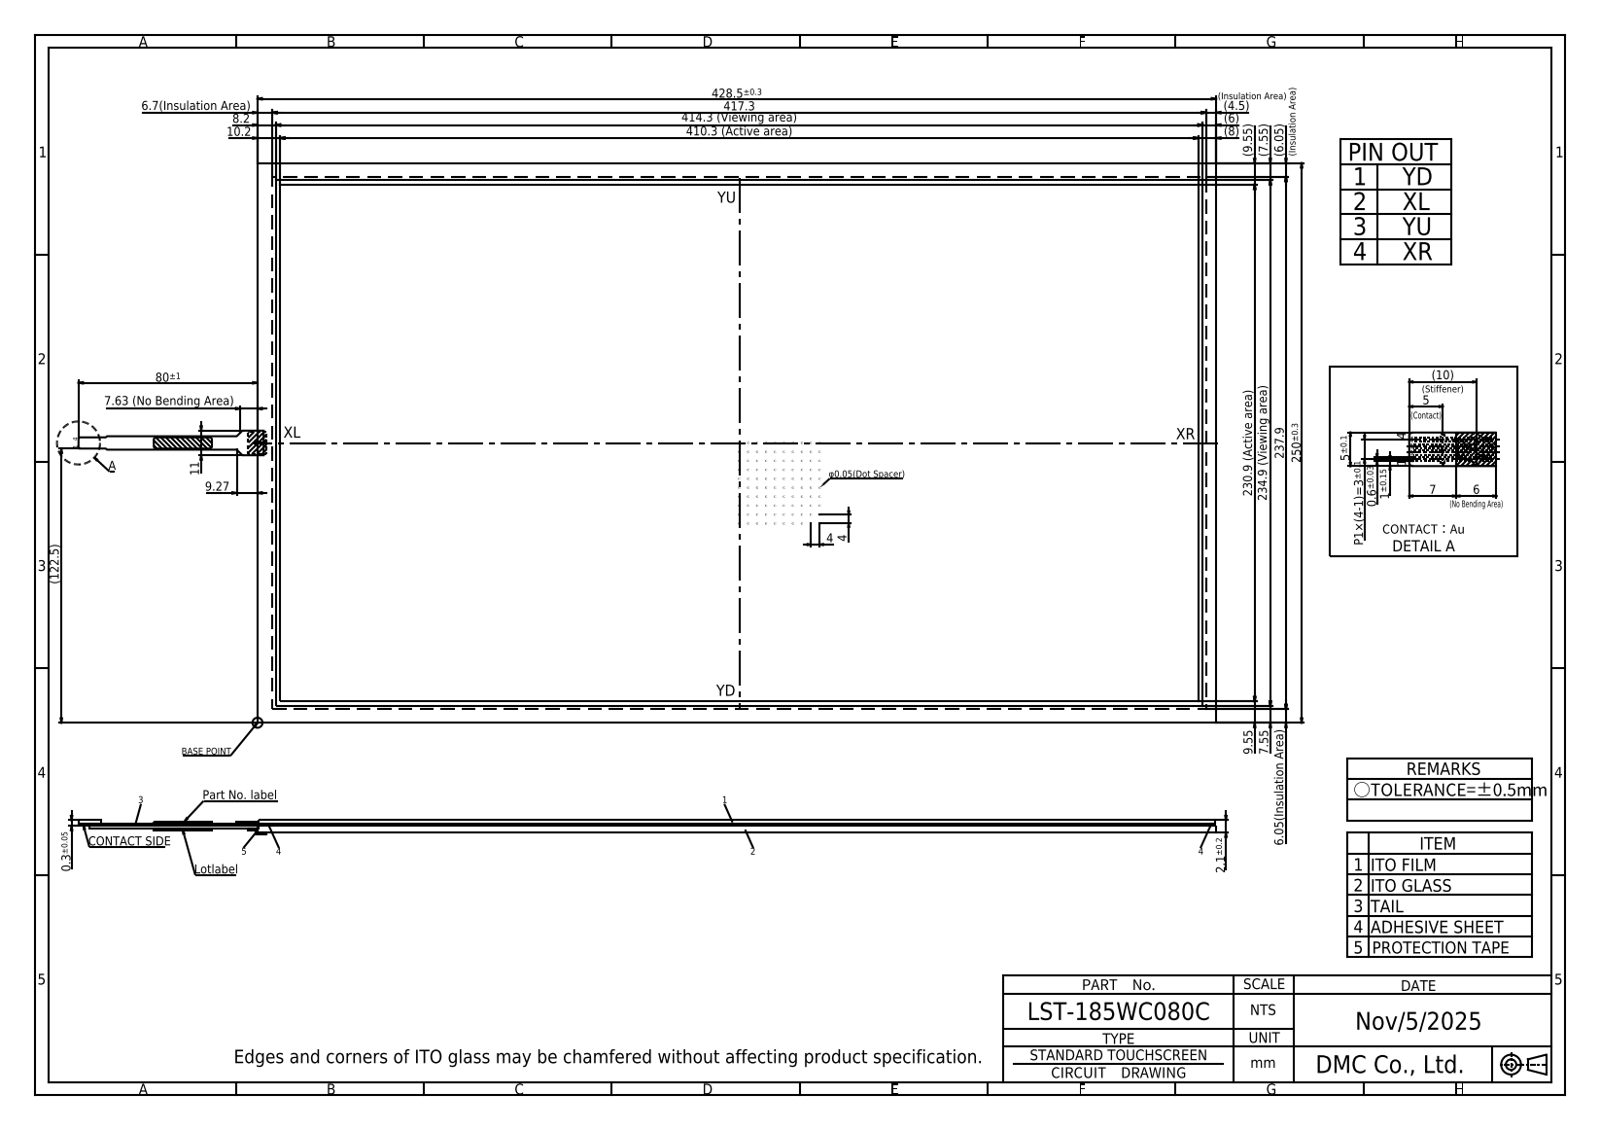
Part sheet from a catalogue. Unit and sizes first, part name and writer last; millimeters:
Units: millimetres
Overall size (bounding box): 599.9 × 350 × 2.6
Partial cylindrical surfaces — rounded edges, fillets, slot ends (radius × count): R0.3 ×4, R0.5 ×2
Main face-to-face distances: 2.1, 2, 250, 428.5, 2.2, 2.3, 7.55, 242.45, 9.55, 240.45
Volume: 224 767 mm³ · Surface area: 218 392 mm²
Bodies: 2 solids, 52 faces (46 planar, 6 cylindrical, 0 other)
Part name (STEP PRODUCT): LST-185WC080C
STEP written by: Autodesk Inventor 2020 (CONFIG_CONTROL_DESIGN)
